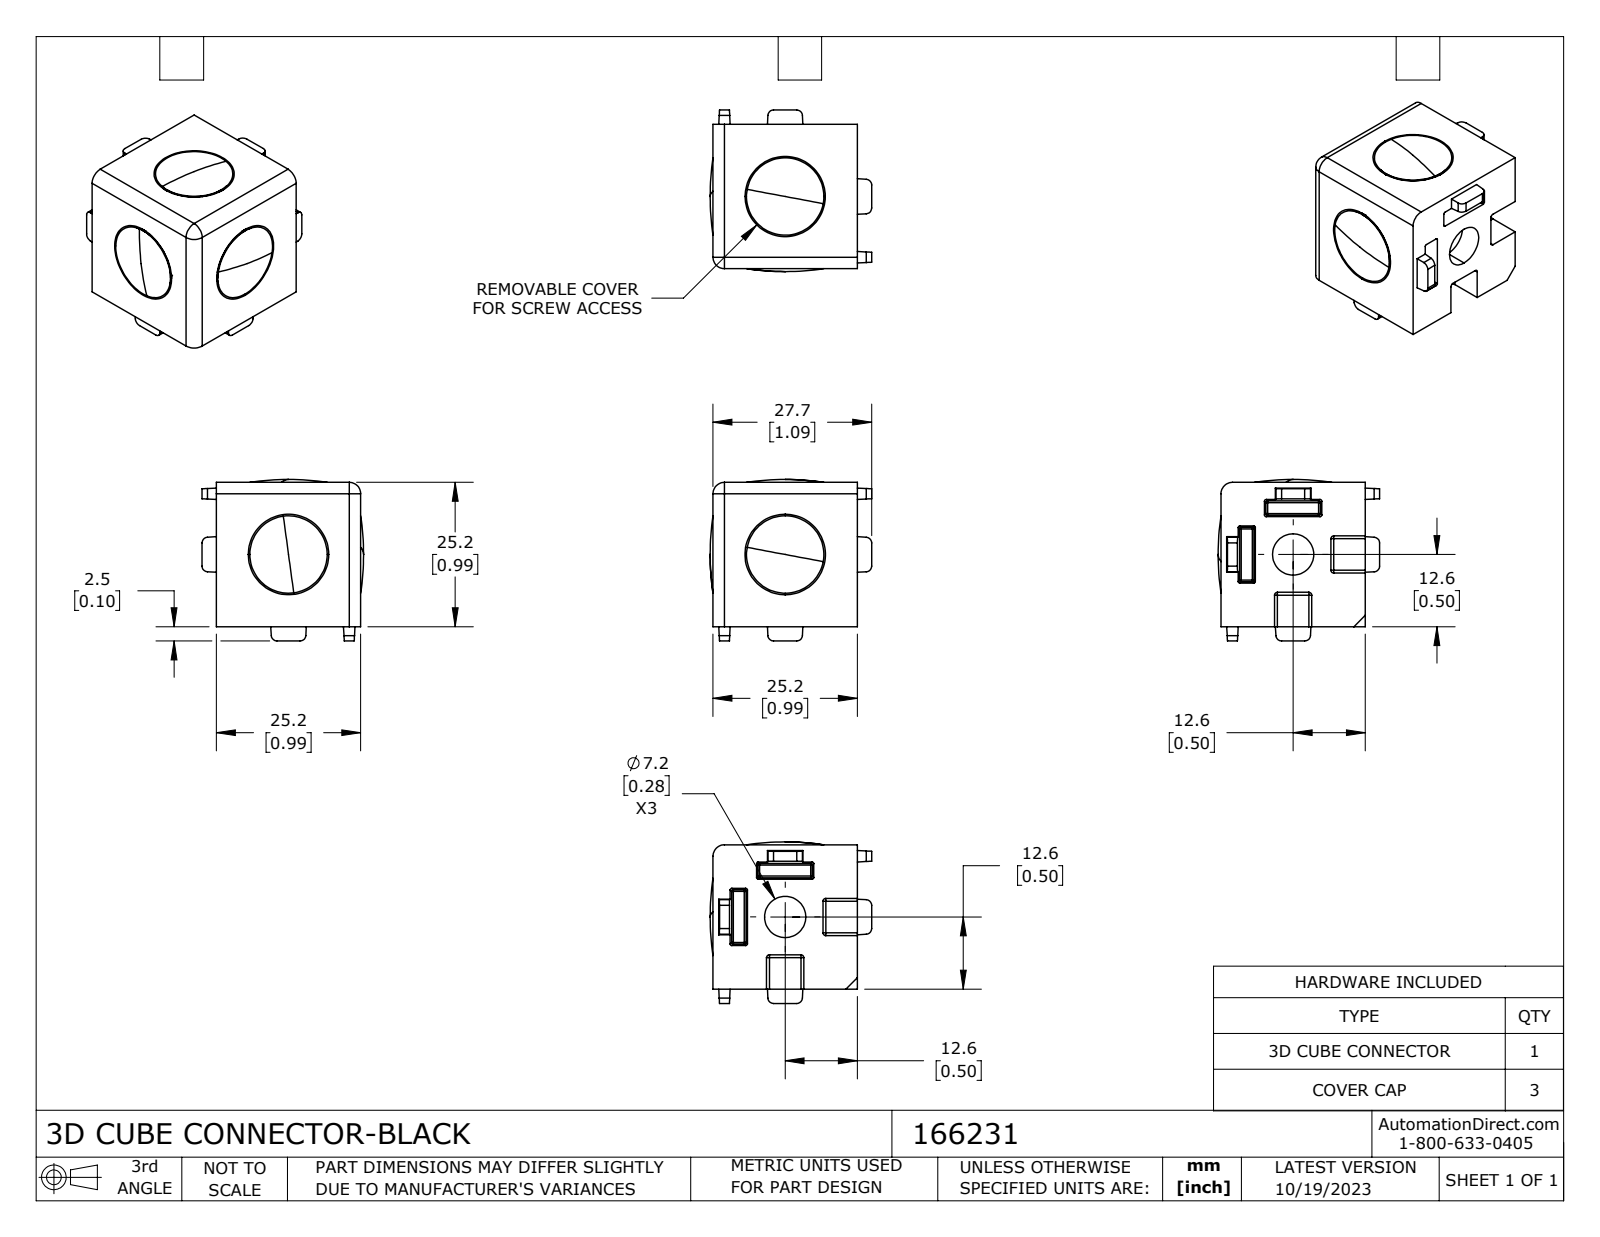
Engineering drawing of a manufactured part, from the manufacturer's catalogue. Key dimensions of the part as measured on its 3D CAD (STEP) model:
Part name (STEP PRODUCT): 166231
STEP written by: SolidWorks 2023 (CONFIG_CONTROL_DESIGN)
Units: millimetres
Bodies: 4 solids, 314 faces (103 planar, 111 cylindrical, 100 other)
Overall size (bounding box): 28.2 × 28.2 × 28.2
Volume: 10 174 mm³ · Surface area: 7 472 mm²
Round holes (diameter × count): ⌀7.2 ×3
Round bosses / shafts (diameter × count): ⌀11 ×3
Partial cylindrical surfaces — rounded edges, fillets, slot ends (radius × count): R0.3 ×48, R1.2 ×18, R0.5 ×15, R1 ×12, R2 ×3
Main face-to-face distances: 25.2, 24.7, 0.5, 4, 21.2, 1, 11.85, 6, 18.7, 19.2
